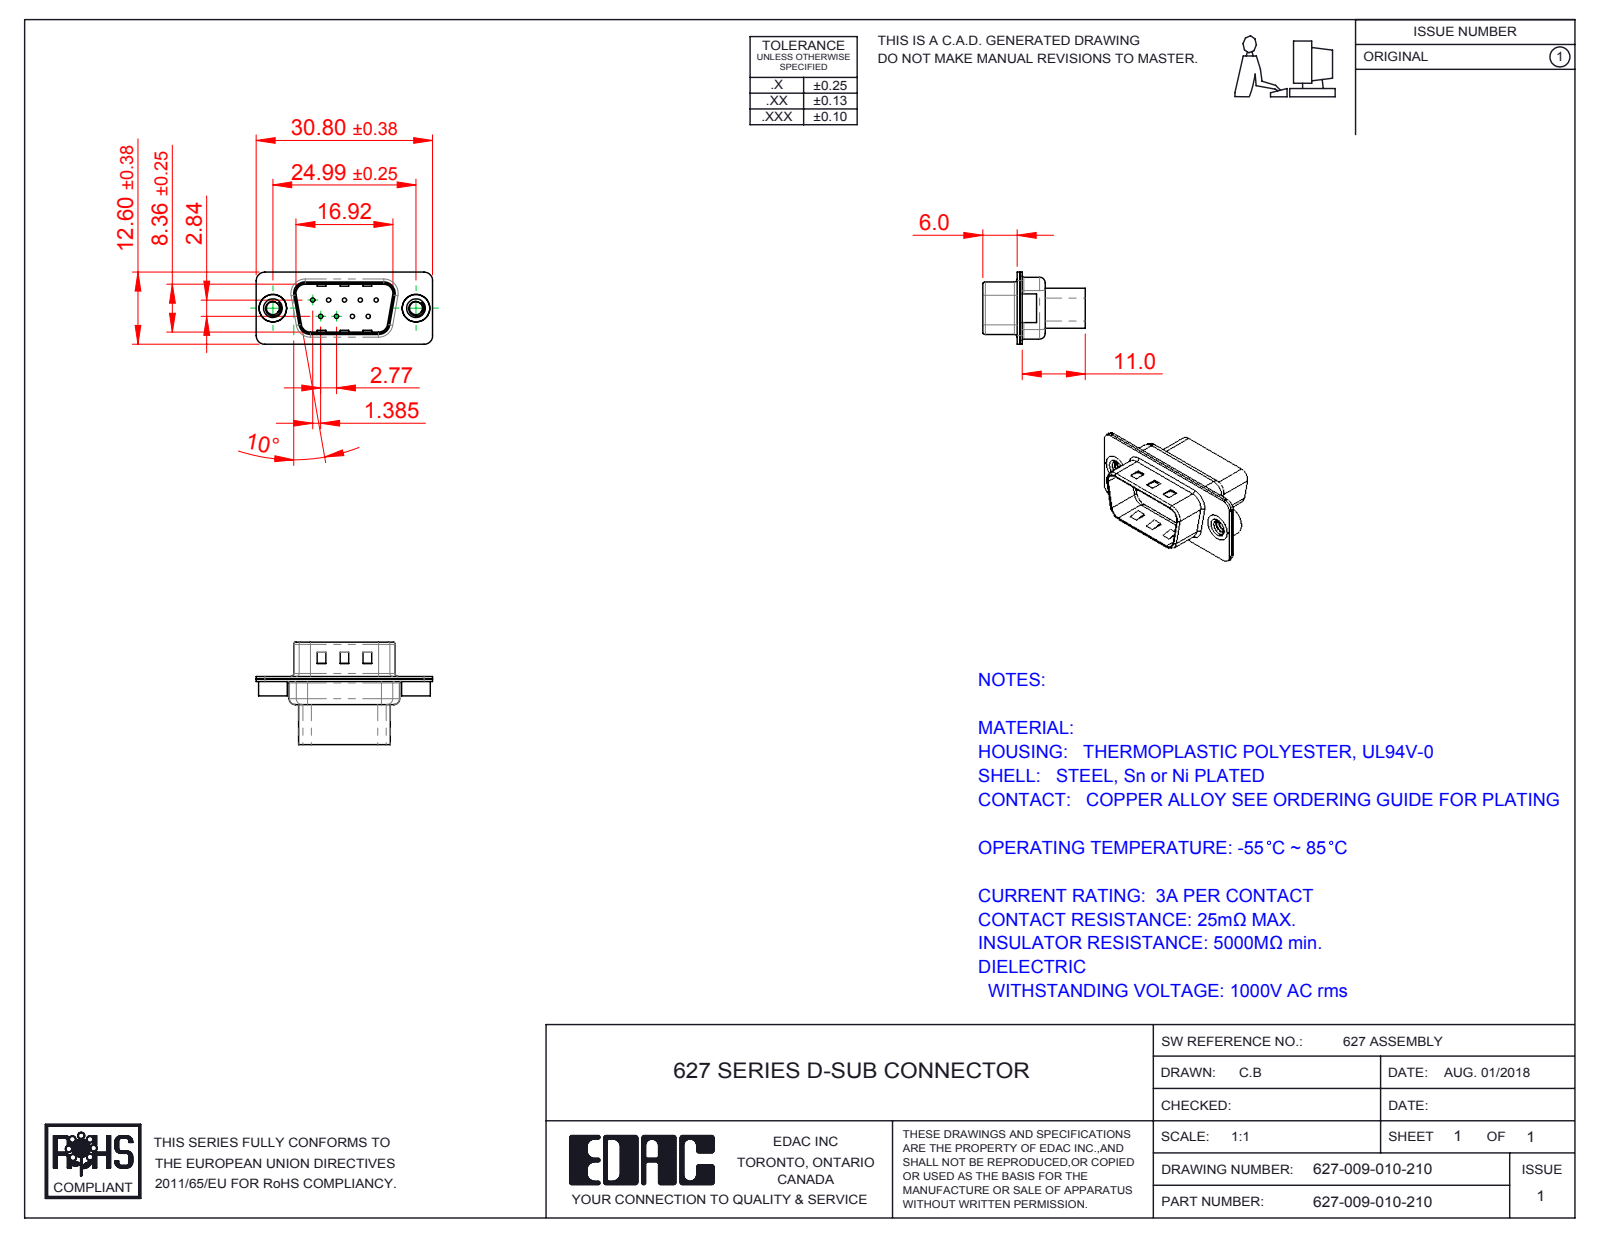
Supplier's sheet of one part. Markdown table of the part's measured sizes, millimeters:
| quantity | value |
| --- | --- |
| part name | 627 Shell Rear_09 Contacts; 627 Shell Front_09 Contacts; 627 Housing_09 HP; 627-009-010-210 (+1 more) |
| STEP written by | SolidWorks 2016 (CONFIG_CONTROL_DESIGN) |
| units | millimeters |
| bodies | 5 solids, 372 faces (125 planar, 181 cylindrical, 66 other) |
| overall size | 30.8 × 17.9 × 12.6 |
| volume | 1 705 mm³ |
| surface area | 3 595 mm² |
| round holes (diameter × count) | 0.75 × 9, 1.6 × 9, 2 × 9, 2.26 × 2, 4 × 2, 4.8 × 2 |
| round bosses / shafts (diameter × count) | 5 × 2, 4.9 × 2 |
| partial cylindrical surfaces (radius × count) | 1.5 × 18, 2 × 12, 0.5 × 8, 1.6 × 8, 0.25 × 4, 0.6 × 4, 0.65 × 4, 0.9 × 4 |
| main face-to-face distances | 0.45, 0.4, 0.9, 0.82, 9.58, 1.4, 0.68, 7.68, 1.08, 8.08 |
| hole center spacings | 3.16, 2.77, 5.54, 5.03, 5.04, 8.31, 7.48, 7.49 |
